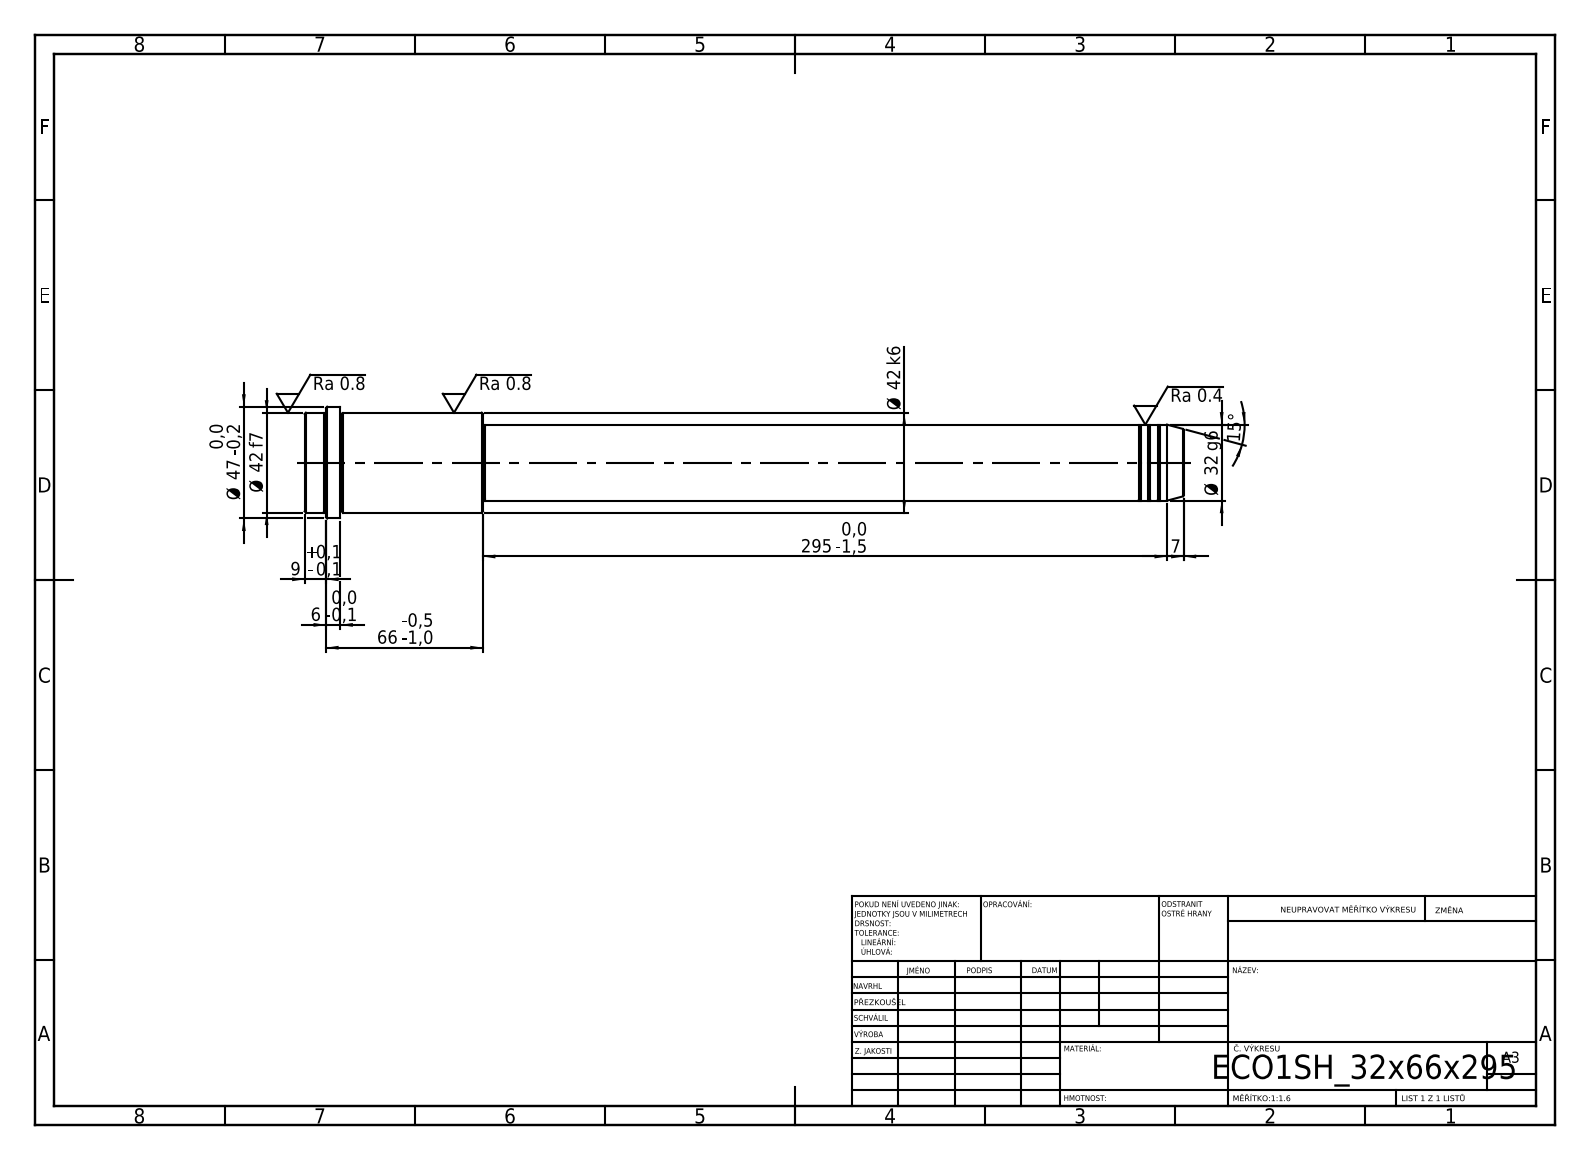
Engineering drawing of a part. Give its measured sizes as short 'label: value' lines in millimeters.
written by: SolidWorks 2019 (CONFIG_CONTROL_DESIGN)
unit: mm
bodies: 1 solid, 52 faces (6 planar, 16 cylindrical, 30 other)
size: 370 × 47 × 47
volume: 342 302 mm³; area: 43 193 mm²
bosses: 1× ⌀47, 1× ⌀42, 1× ⌀32, 1× ⌀31
face distances: 370, 295, 75, 355, 60, 15, 361, 66, 6, 9
